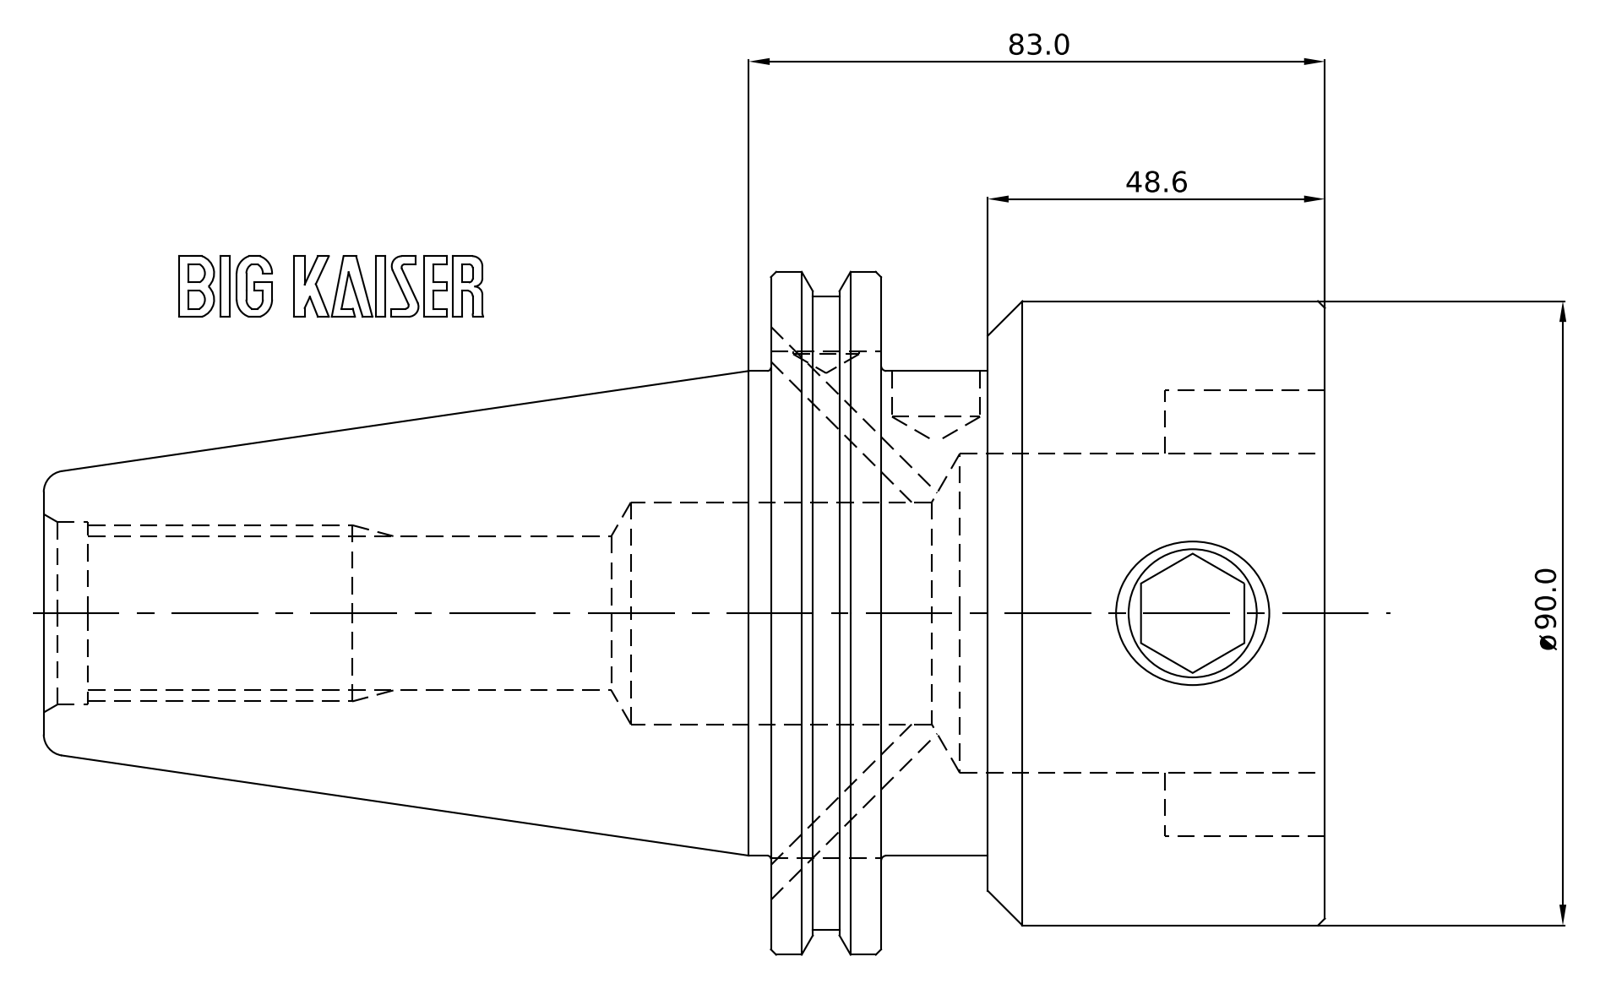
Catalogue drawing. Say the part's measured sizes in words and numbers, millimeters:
The part is named "11.326.974". Its 3-D file was written by "SolidWorks 2021 (CONFIG_CONTROL_DESIGN)". It is 1 solid with 16 faces: 7 planar, 6 cylindrical and 3 other. Overall it measures 184.61 by 98.43 by 98.43 millimeters. Its volume is 747 836 cubic millimeters and its surface area 59 603 square millimeters. Round bosses or shafts: 1 of diameter 98.43, 1 of diameter 91.29, 1 of diameter 89.99, 1 of diameter 69.85. The main face-to-face distances are 81.51, 63.96, 17.55, 48.01, 15.95, 33.5, 184.61, 136.6, 120.65, 103.1.
